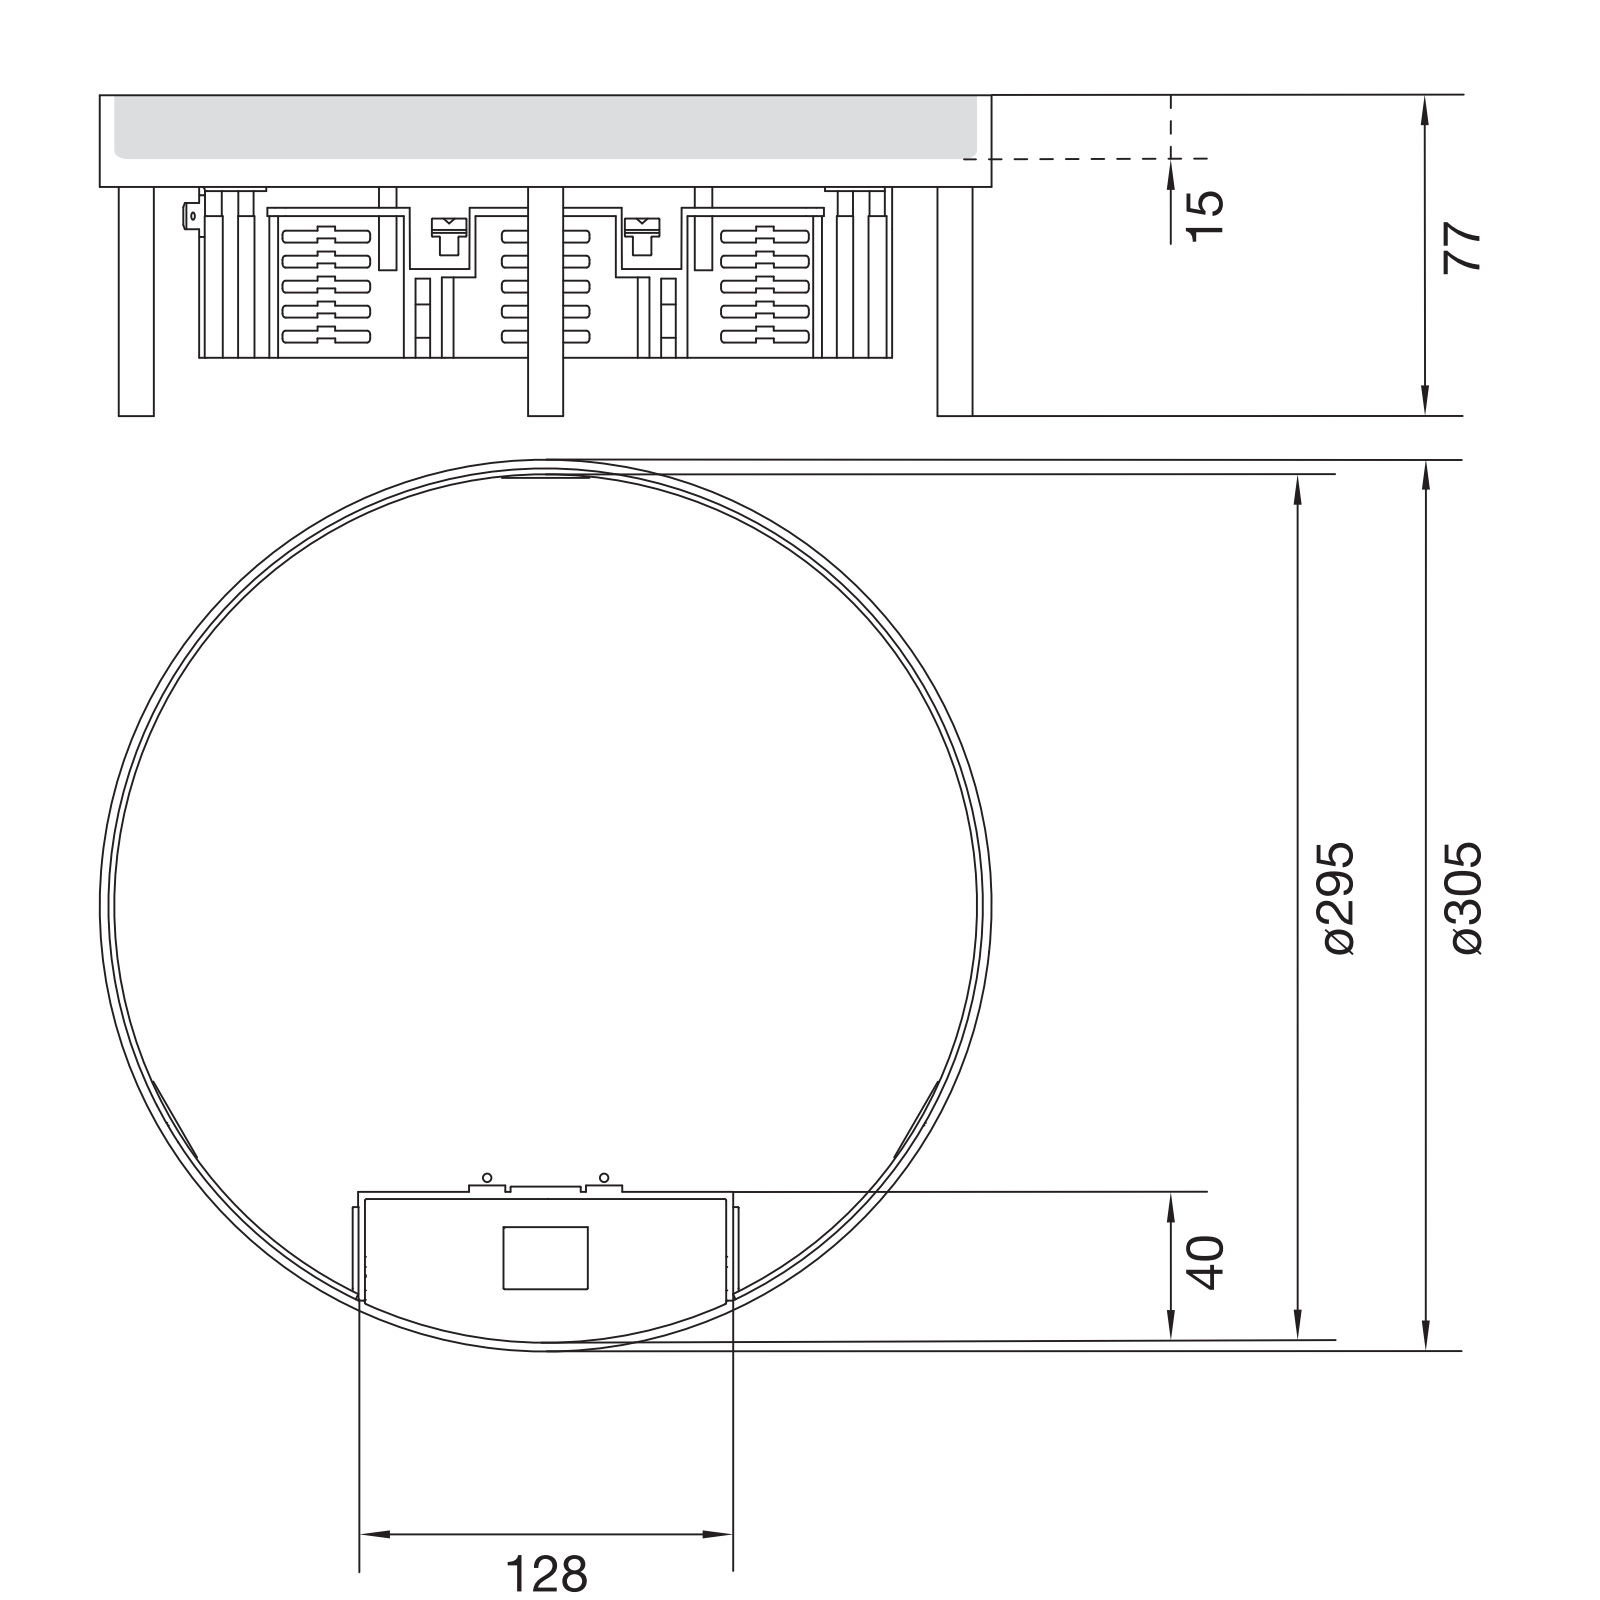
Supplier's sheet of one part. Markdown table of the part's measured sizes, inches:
| quantity | value |
| --- | --- |
| part name | T-00702; T-00703; T-00704; T-00708 (+8 more) |
| STEP written by | CREO PARAMETRIC BY PTC INC, 2022024 (AUTOMOTIVE_DESIGN) |
| units | inches |
| bodies | 15 solids, 271 faces (170 planar, 85 cylindrical, 16 other) |
| overall size | 12.008 × 12.008 × 3.031 |
| volume | 22.17 in³ |
| surface area | 560.2 in² |
| round holes (diameter × count) | 0.15 × 6, 0.268 × 4, 0.335 × 4, 0.398 × 4, 0.098 × 2 |
| round bosses / shafts (diameter × count) | 0.472 × 4, 0.388 × 4, 12.008 × 1, 11.85 × 1, 11.772 × 1, 11.614 × 1 |
| partial cylindrical surfaces (radius × count) | 0.02 × 10, 0.012 × 3, 0.04 × 1, 0.26 × 1, 5.906 × 1 |
| main face-to-face distances | 0.079, 0.197, 0.098, 0.118, 0.276, 8.996, 9.035, 0.669, 0.591, 0.787 |
| hole center spacings | 2.343, 5.654, 7.795, 8.879, 10.262, 0.996, 1.592, 2.007 |
